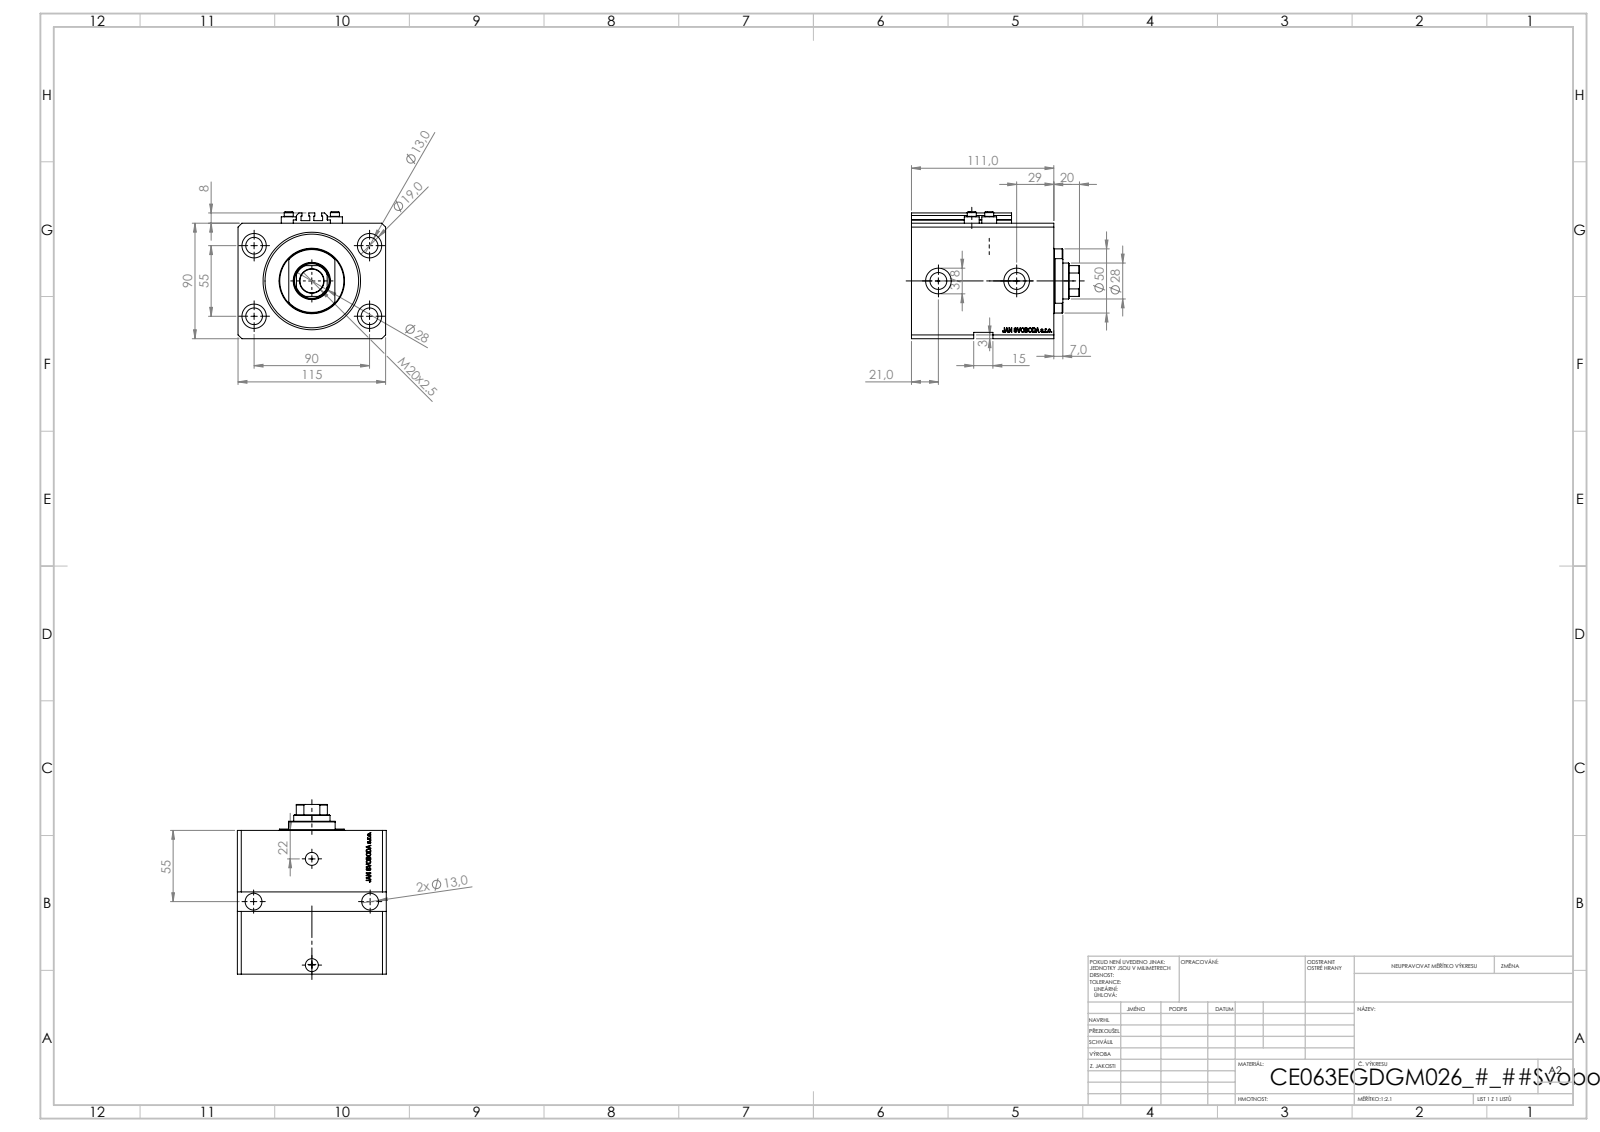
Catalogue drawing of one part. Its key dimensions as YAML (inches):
part_name: "V250CE_VC_E; V250CE_E_Body; ALLEN BOLT V250CE; V250CE_C_VCP"
step_written_by: "SolidWorks 2019 (CONFIG_CONTROL_DESIGN)"
units: inches
bodies: {solids: 8, faces: 1123, planar: 547, cylindrical: 138, other: 438}
overall_size: [5.157, 4.528, 3.898]
volume: 60.75
surface_area: 249.3
round_holes:
  - {diameter: 0.512, count: 6}
  - {diameter: 0.049, count: 4}
  - {diameter: 0.157, count: 4}
  - {diameter: 0.748, count: 4}
  - {diameter: 0.394, count: 2}
  - {diameter: 0.518, count: 2}
  - {diameter: 0.787, count: 2}
  - {diameter: 0.728, count: 1}
  - {diameter: 1.102, count: 1}
  - {diameter: 2.48, count: 1}
  - {diameter: 2.992, count: 1}
round_bosses_or_shafts:
  - {diameter: 0.457, count: 4}
  - {diameter: 0.276, count: 4}
  - {diameter: 1.969, count: 1}
partial_cylinders:
  - {radius: 0.008, count: 10}
  - {radius: 0.531, count: 1}
face_to_face_distances: [3.543, 4.528, 4.37, 3.665, 0.787, 0.705, 3.583, 2.878, 1.811, 2.559]
hole_center_spacings: [2.076, 3.543, 0.535, 1.078, 1.12, 1.324, 1.417, 1.515]
